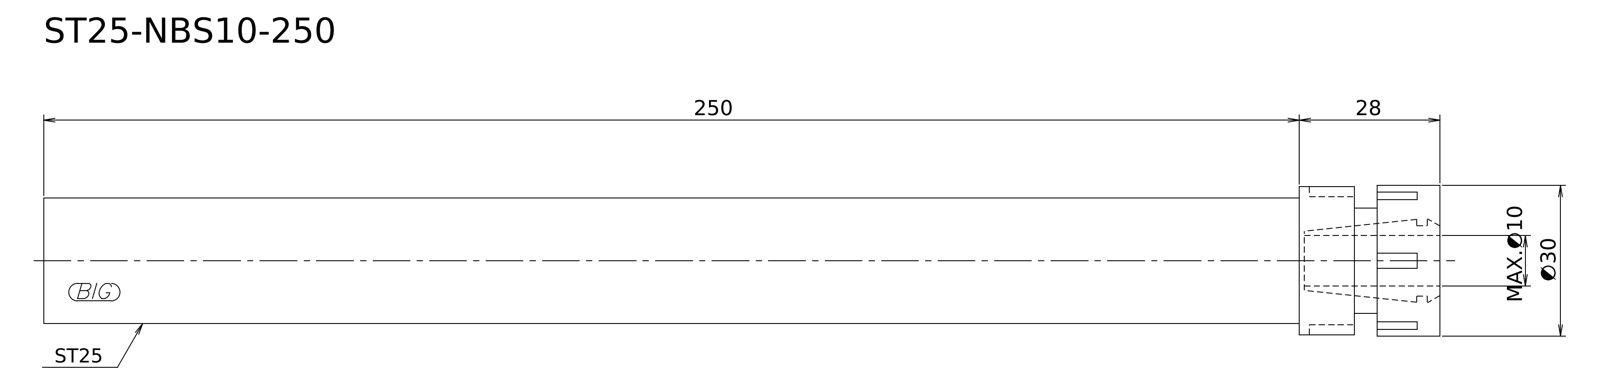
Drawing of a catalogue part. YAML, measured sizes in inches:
step_written_by: "Kubotek KeyCreator V8.5.1 (14335) (CONFIG_CONTROL_DESIGN)"
units: inches
bodies: {solids: 1, faces: 9, planar: 5, cylindrical: 4, other: 0}
overall_size: [10.945, 1.181, 1.181]
volume: 8.582
surface_area: 37.54
round_bosses_or_shafts:
  - {diameter: 1.181, count: 1}
  - {diameter: 1.161, count: 1}
  - {diameter: 0.984, count: 1}
  - {diameter: 0.827, count: 1}
face_to_face_distances: [10.945, 0.492, 10.453, 0.669, 0.177, 10.276, 1.102, 0.61, 0.433, 9.843]
